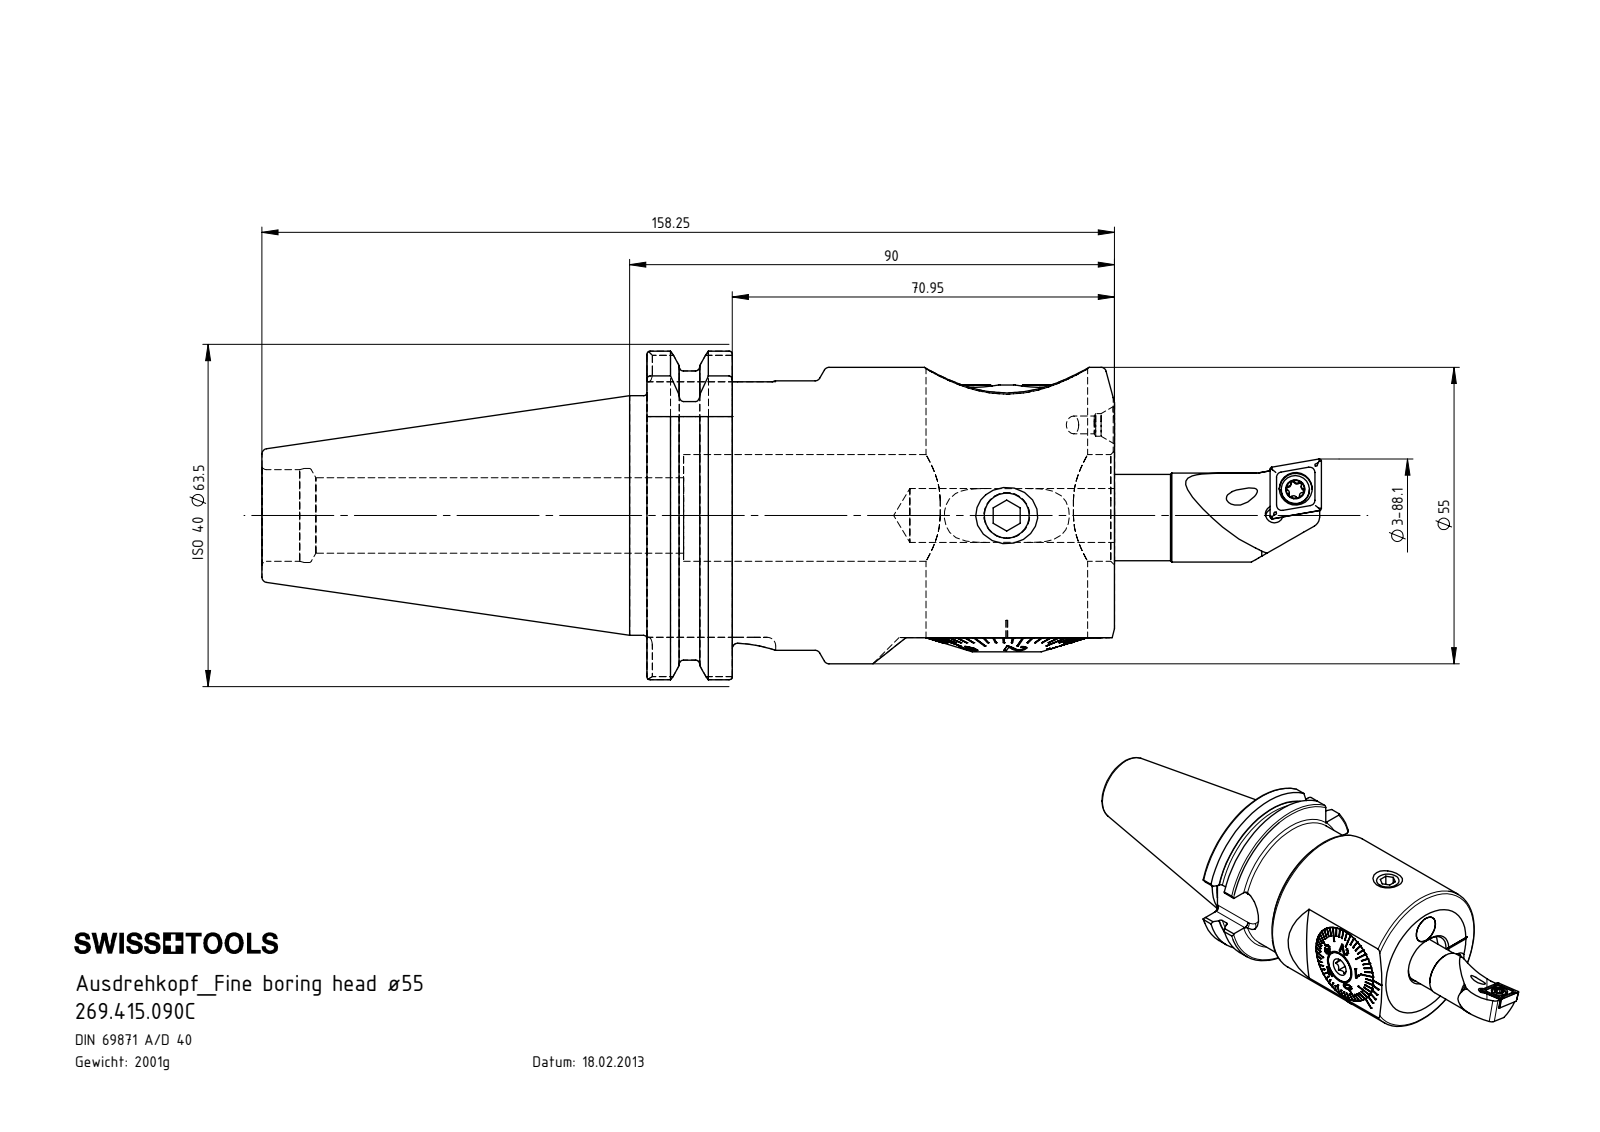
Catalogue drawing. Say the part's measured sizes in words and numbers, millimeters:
The part is named "Klebstoff D10; A55-BG1.014.041; A55-BG2.015.007_B; A55-BG2.014.007_A (+8 more)". Its 3-D file was written by "SolidWorks 2017 (CONFIG_CONTROL_DESIGN)". It is 19 solids with 956 faces: 390 planar, 194 cylindrical and 372 other. Overall it measures 196.66 by 63.5 by 60.94 millimeters. Its volume is 255 189 cubic millimeters and its surface area 63 680 square millimeters. Round holes: 3 of diameter 3.3, 3 of diameter 8.5, 2 of diameter 3, 2 of diameter 14, 1 of diameter 1, 1 of diameter 1.6, 1 of diameter 2, 1 of diameter 4.2, 1 of diameter 4.4, 1 of diameter 6.1, 1 of diameter 8, 1 of diameter 10. Round bosses or shafts: 3 of diameter 10, 2 of diameter 5.25, 2 of diameter 4, 1 of diameter 55, 1 of diameter 50, 1 of diameter 44.45, 1 of diameter 30, 1 of diameter 29.98. Partial cylindrical surfaces (rounded edges, fillets, slot ends): 12 of radius 0.34, 12 of radius 0.59, 8 of radius 1.6, 3 of radius 3.2, 1 of radius 0.5, 1 of radius 2, 1 of radius 3.5, 1 of radius 8. The main face-to-face distances are 86.8, 15.85, 70.95, 5.3, 6.48, 1.18, 2.8, 2.5, 3.68, 22. The hole center spacings are 14.5, 7.25, 0.37, 6.07, 6.19, 14.7, 15.07, 18.83.
